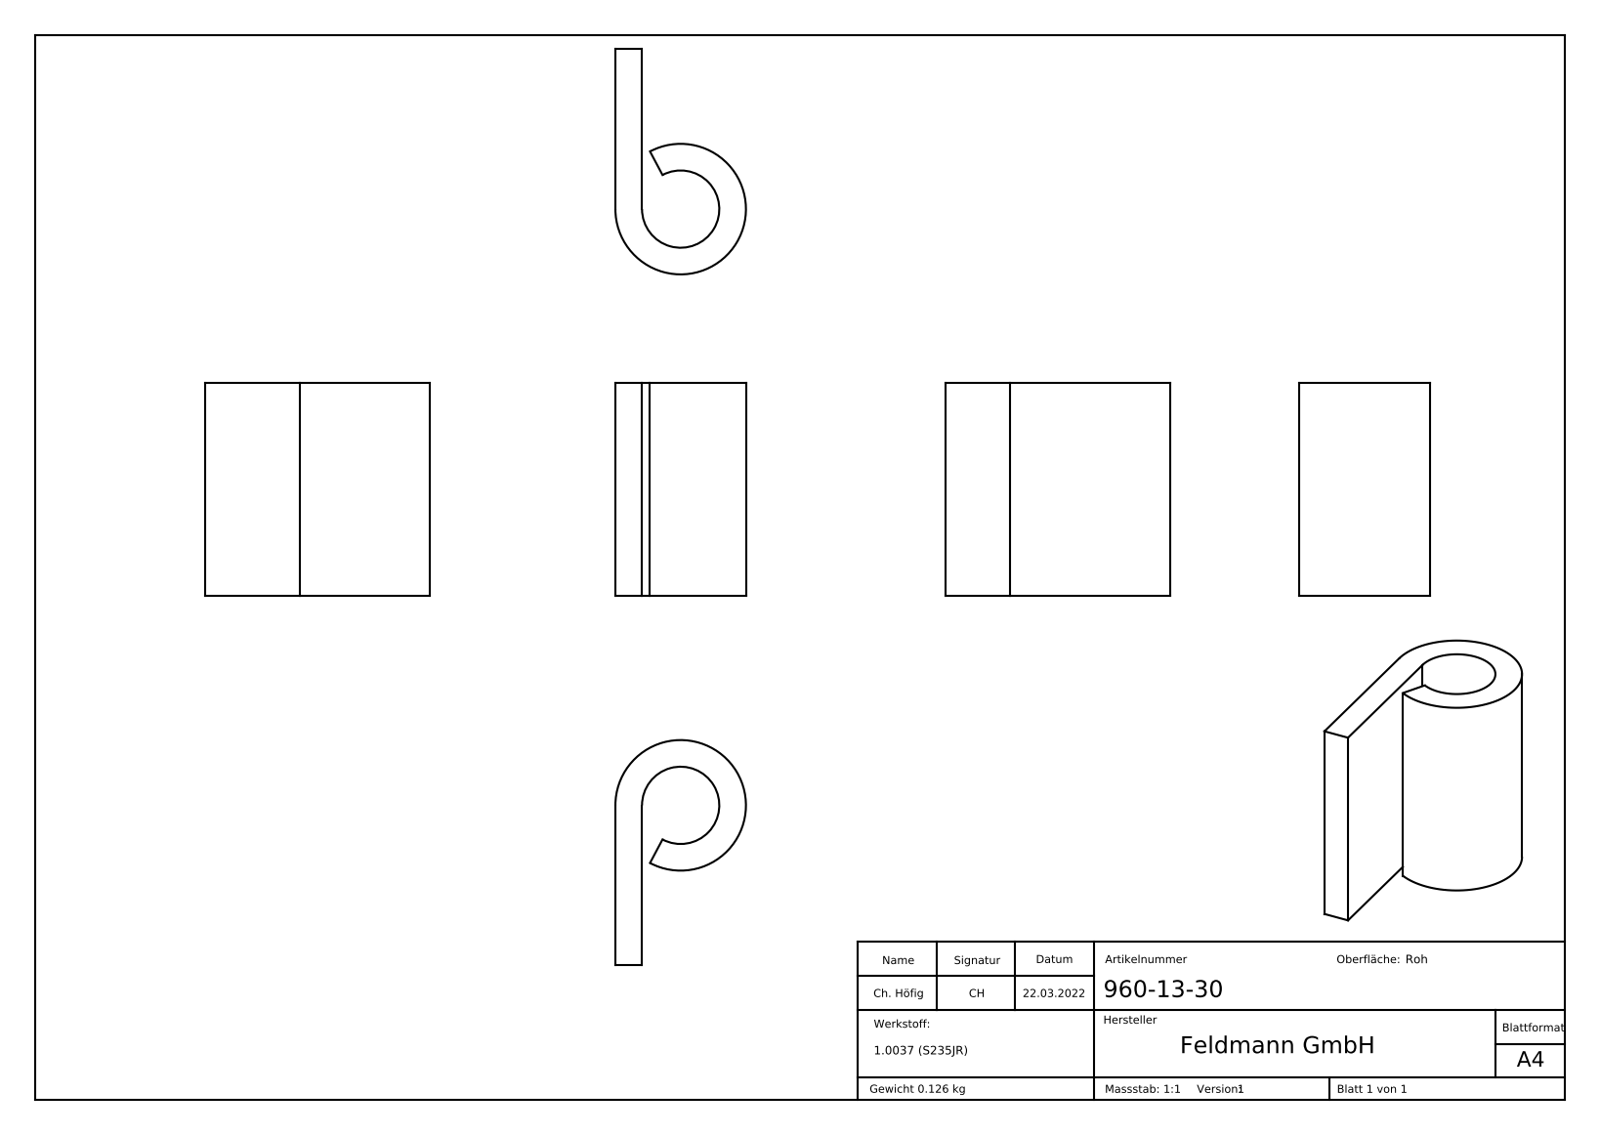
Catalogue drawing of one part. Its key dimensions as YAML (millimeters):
part_name: "960-13-30"
step_written_by: "SolidWorks 2018 (CONFIG_CONTROL_DESIGN)"
units: millimeters
bodies: {solids: 1, faces: 224, planar: 110, cylindrical: 2, other: 112}
overall_size: [42.25, 40, 24.5]
volume: 16141
surface_area: 7673
round_holes:
  - {diameter: 14.5, count: 1}
round_bosses_or_shafts:
  - {diameter: 24.5, count: 1}
face_to_face_distances: [5, 40, 2.97, 1.25, 1.64, 0.39, 5.73, 2.02, 0.58, 1.37]
